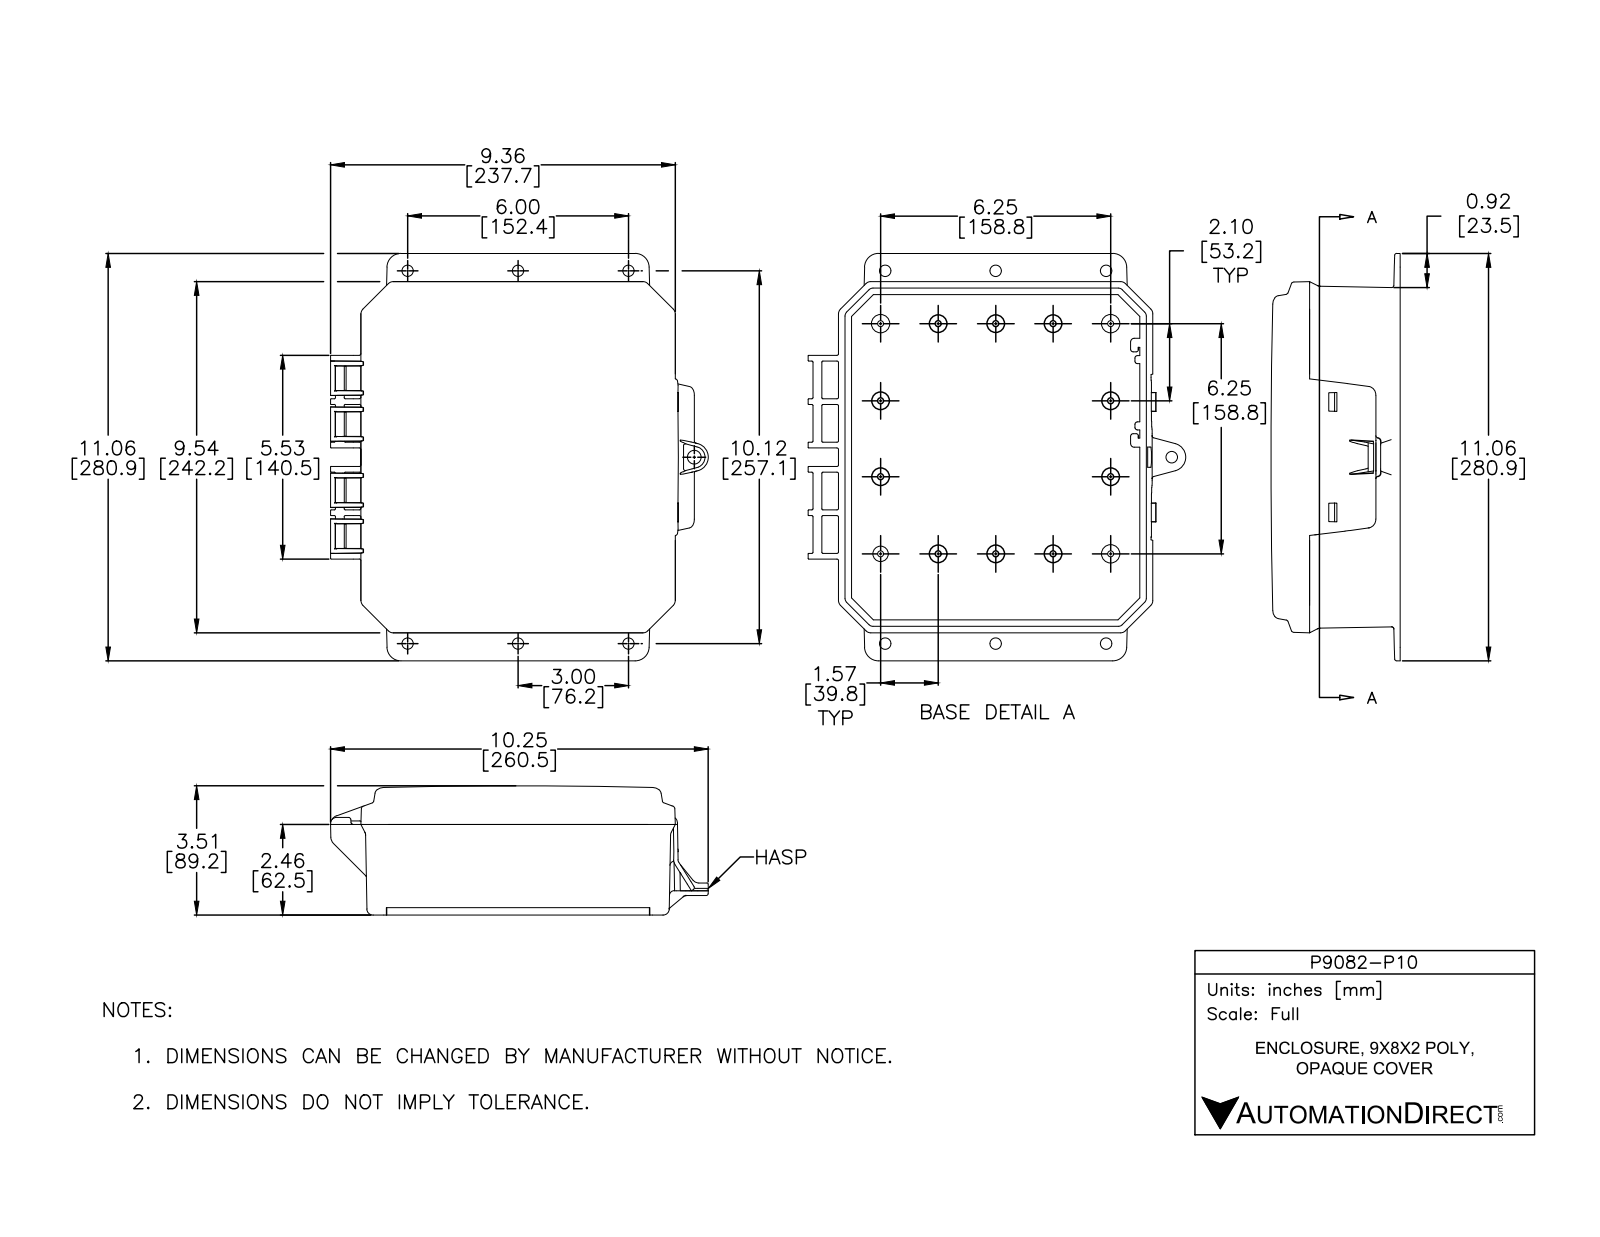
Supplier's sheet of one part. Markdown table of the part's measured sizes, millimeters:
| quantity | value |
| --- | --- |
| part name | P9082; P982BH; P98CHO |
| STEP written by | SolidWorks 2016 (AUTOMOTIVE_DESIGN) |
| units | millimeters |
| bodies | 2 solids, 1756 faces (407 planar, 674 cylindrical, 675 other) |
| overall size | 280.9 × 260.5 × 89.2 |
| volume | 755 600 mm³ |
| surface area | 411 600 mm² |
| round holes (diameter × count) | 4.1 × 14 |
| round bosses / shafts (diameter × count) | 6.1 × 1 |
| partial cylindrical surfaces (radius × count) | 0.5 × 84, 1 × 72, 0.8 × 64, 0.4 × 60, 1.5 × 40, 0.3 × 37, 1.3 × 24, 4.8 × 17 |
| main face-to-face distances | 3.8, 12, 9.5, 62.5, 58.7, 2.5, 3, 195.9, 207.9, 233.3 |
| hole center spacings | 158.8, 39.6, 39.8, 53.2, 66.4, 79.4, 95.6, 105.5 |
